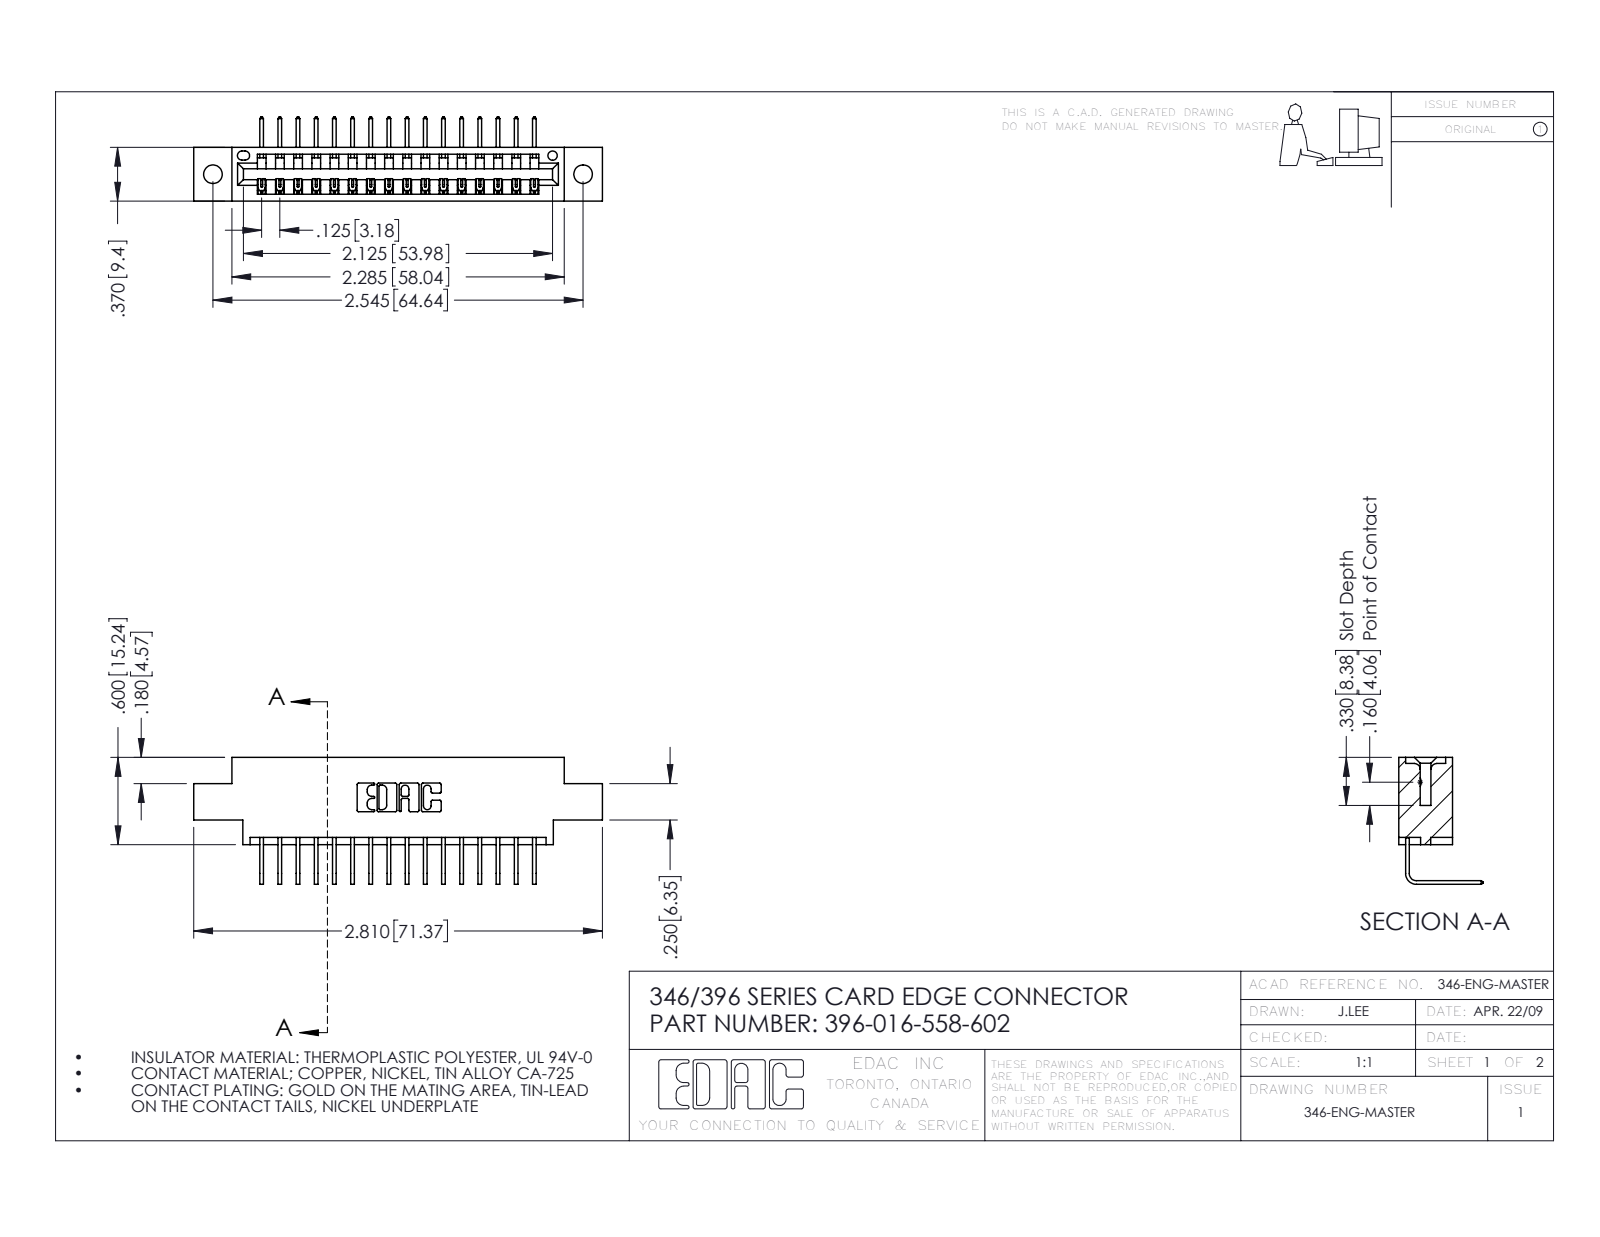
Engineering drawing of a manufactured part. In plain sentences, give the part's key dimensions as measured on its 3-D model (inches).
The part is named "345-292-001_558 Tail - 2; 346 Part_0.170 Offset - 0.128 Dia; 396-016-558-602". Its 3-D file was written by "SolidWorks 2016 (CONFIG_CONTROL_DESIGN)". It is 17 solids with 1086 faces: 752 planar, 334 cylindrical and 0 other. Overall it measures 2.81 by 0.873 by 0.58 inches. Its volume is 0.398 cubic inches and its surface area 12.51 square inches. Round holes: 2 of diameter 0.128, 1 of diameter 0.064. Partial cylindrical surfaces (rounded edges, fillets, slot ends): 32 of radius 0.006, 22 of radius 0.01, 6 of radius 0.007, 6 of radius 0.031, 3 of radius 0.026, 2 of radius 0.031, 2 of radius 0.04, 1 of radius 0.014. The main face-to-face distances are 0.322, 0.37, 0.048, 0.25, 0.298, 0.025, 0.072, 0.148, 0.222, 0.1. The hole center spacings are 0.246, 2.338, 2.545.
